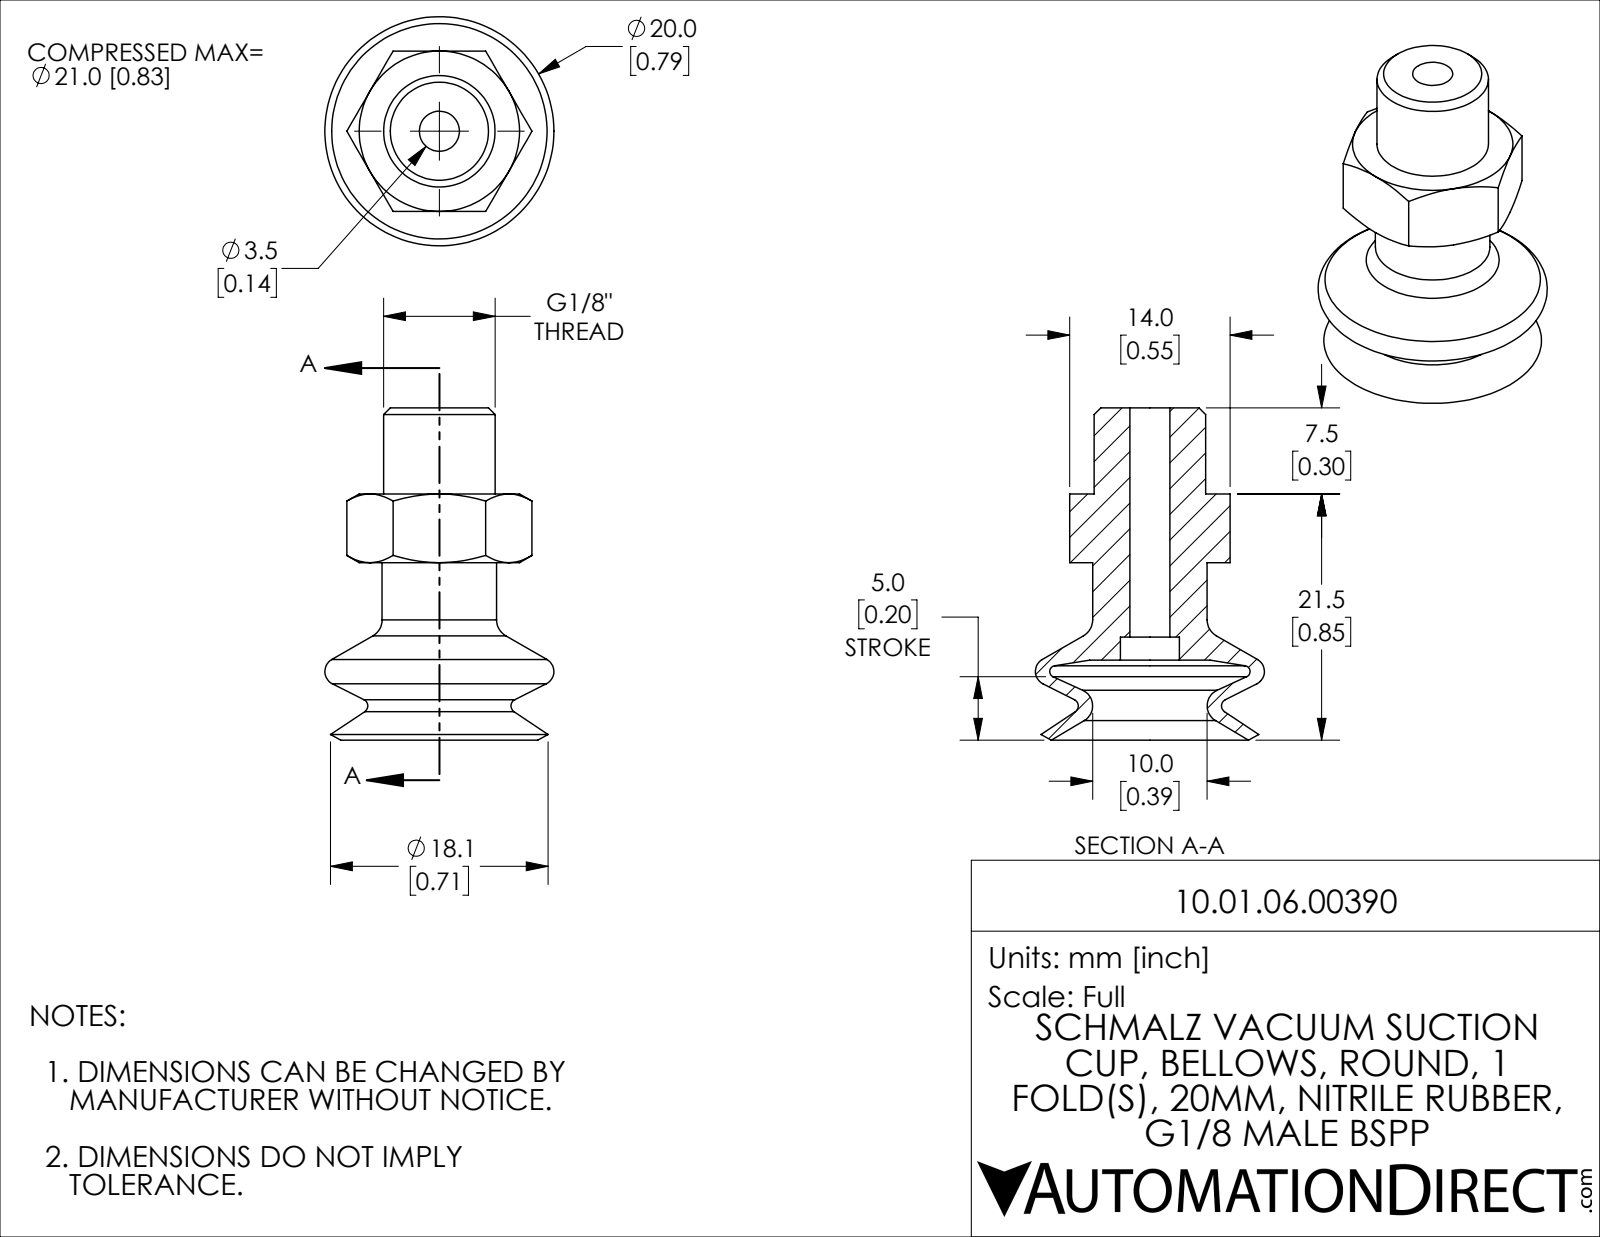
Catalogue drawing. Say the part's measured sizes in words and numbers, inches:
The part is named "10.01.06.00390". Its 3-D file was written by "SolidWorks 2021 (CONFIG_CONTROL_DESIGN)". It is 1 solid with 63 faces: 11 planar, 8 cylindrical and 44 other. Overall it measures 1.142 by 0.787 by 0.787 inches. Its volume is 0.172 cubic inches and its surface area 4.148 square inches. Round holes: 1 of diameter 0.138, 1 of diameter 0.203. Round bosses or shafts: 1 of diameter 0.394, 1 of diameter 0.383. The main face-to-face distances are 0.551, 0.236, 0.335, 0.571, 0.866, 0.531, 0.295, 0.079, 0.256, 0.492.
